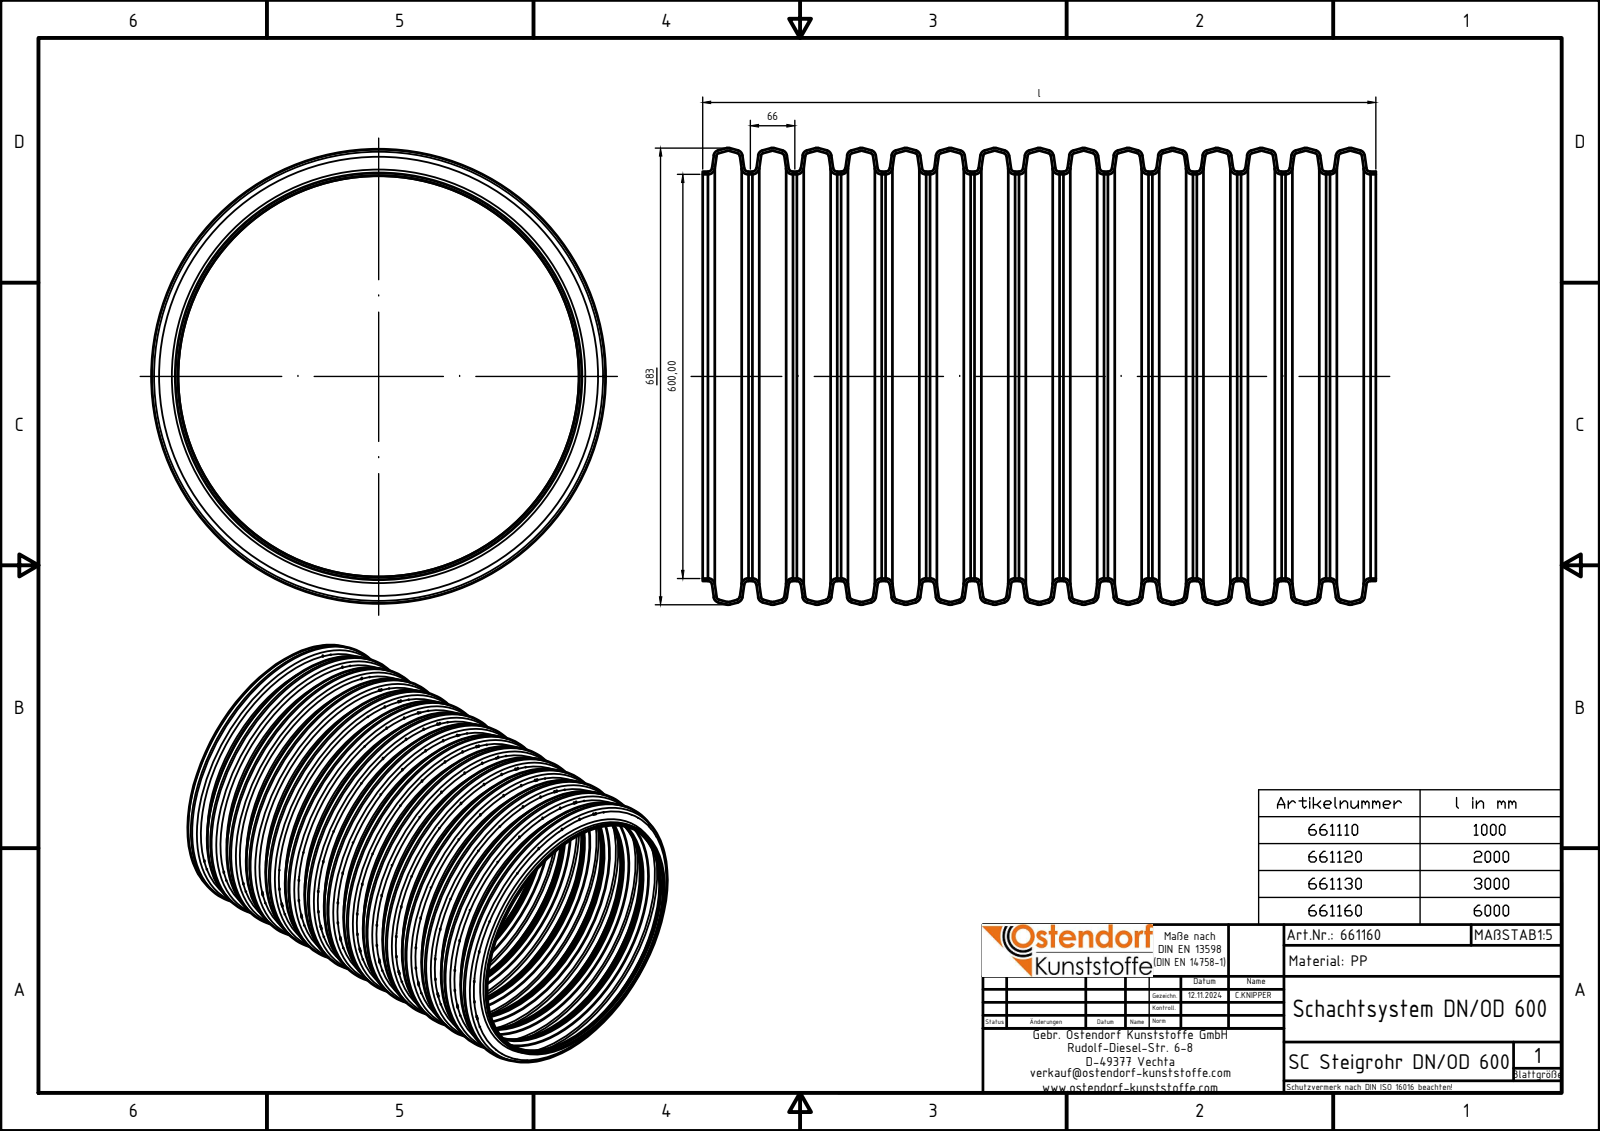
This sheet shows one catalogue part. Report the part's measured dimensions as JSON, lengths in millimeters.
{"part_name": "661160z", "step_written_by": "Autodesk Inventor 2024 (AUTOMOTIVE_DESIGN)", "units": "millimeters", "bodies": {"solids": 1, "faces": 1822, "planar": 2, "cylindrical": 182, "other": 1638}, "overall_size": [6000, 678.36, 678.36], "volume_mm3": 83030000, "surface_area_mm2": 41490000, "round_holes": [[600, 1]], "round_bosses_or_shafts": [[607.99, 1]], "face_to_face_distances": [6000]}
